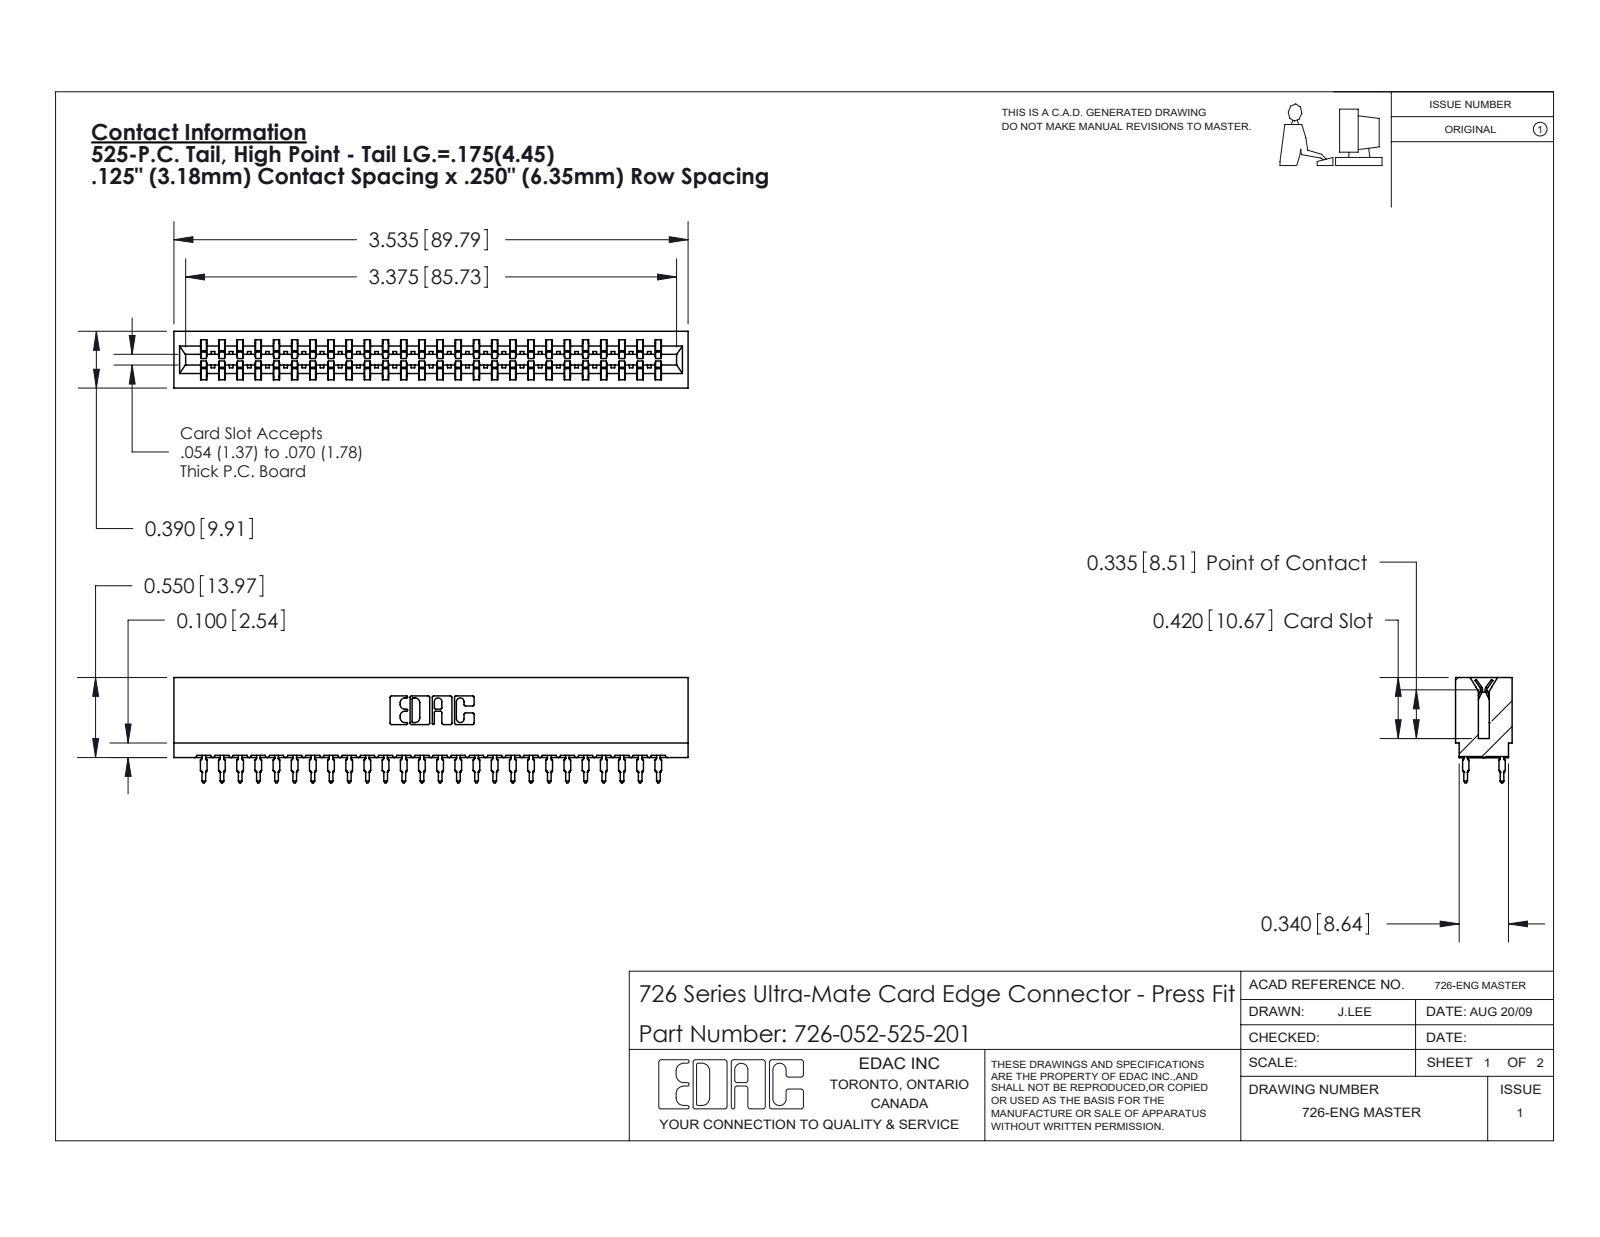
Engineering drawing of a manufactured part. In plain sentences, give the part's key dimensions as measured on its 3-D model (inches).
The part is named "726 Part_.515 Slot Depth - 01; 726-052-525-201; 746-292-001_525". Its 3-D file was written by "SolidWorks 2020 (CONFIG_CONTROL_DESIGN)". It is 53 solids with 4751 faces: 2447 planar, 952 cylindrical and 1352 other. Overall it measures 3.535 by 0.724 by 0.39 inches. Its volume is 0.508 cubic inches and its surface area 20.87 square inches. Partial cylindrical surfaces (rounded edges, fillets, slot ends): 104 of radius 0.021, 27 of radius 0.015, 22 of radius 0.01, 8 of radius 0.005, 8 of radius 0.011, 6 of radius 0.007, 6 of radius 0.031, 3 of radius 0.026. The main face-to-face distances are 0.057, 0.333, 0.25, 0.39, 0.025, 0.307, 0.275, 0.5, 0.125, 0.083.
